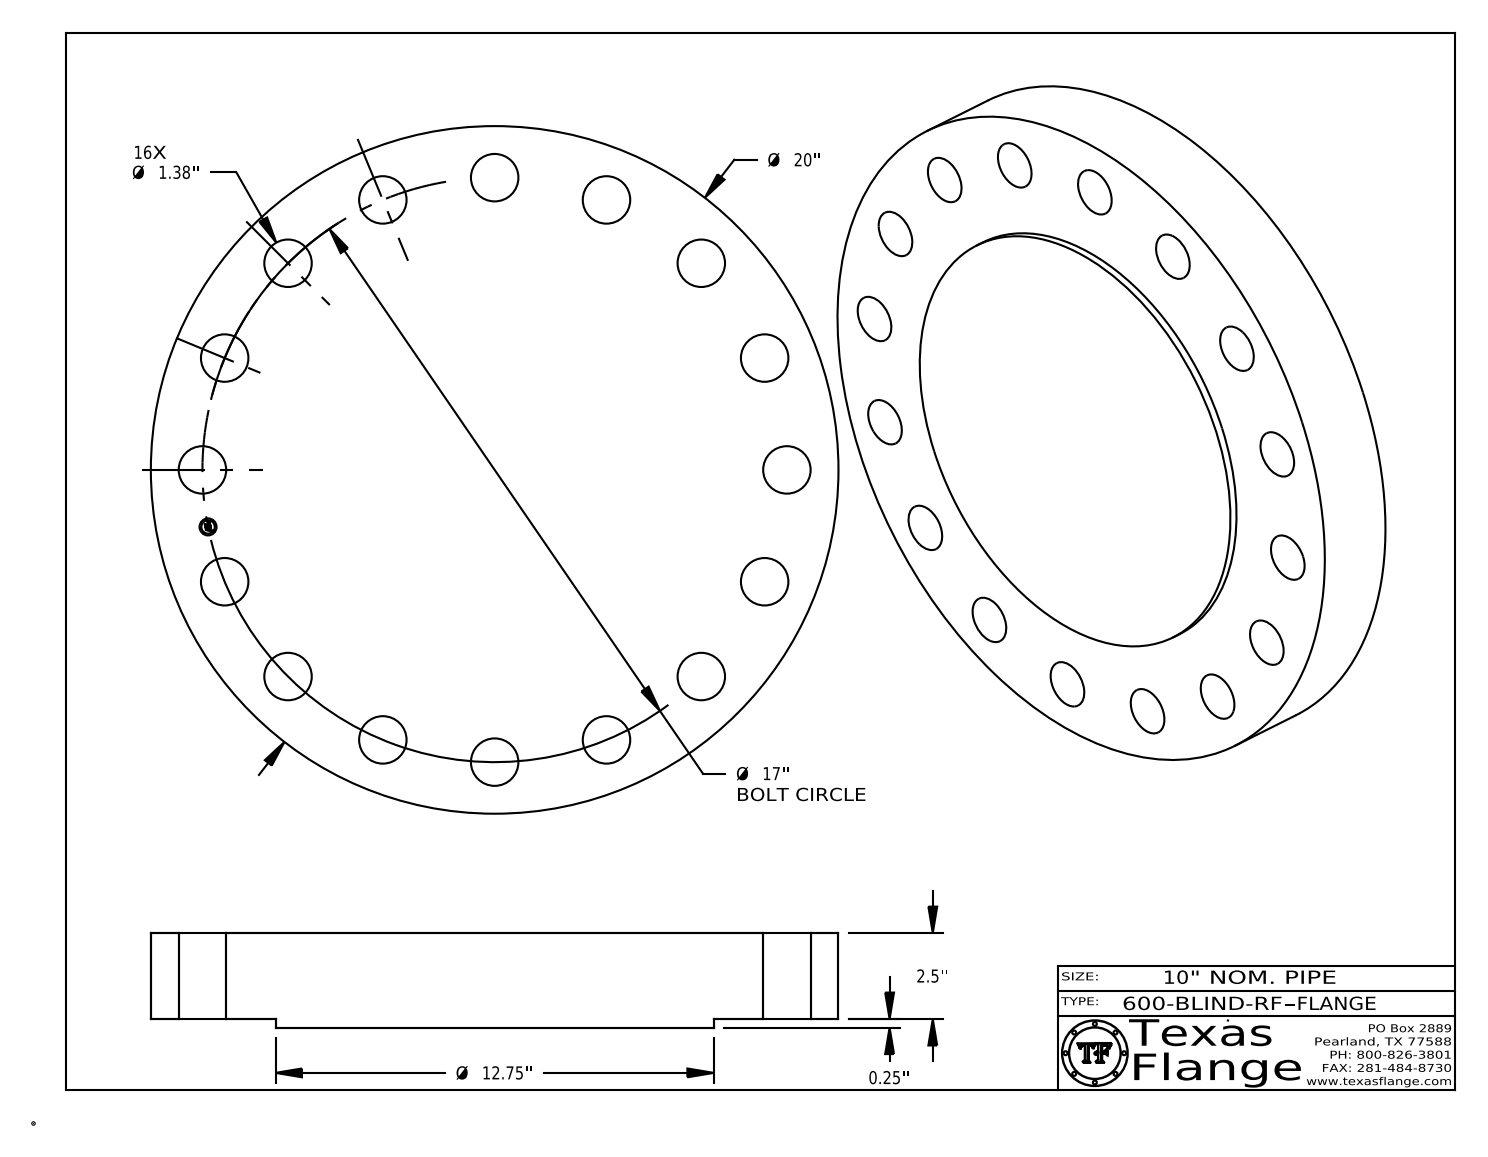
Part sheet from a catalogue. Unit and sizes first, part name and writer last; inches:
Units: inches
Overall size (bounding box): 20 × 20 × 2.75
Round holes (diameter × count): ⌀1.38 ×16, ⌀0.495 ×1
Round bosses / shafts (diameter × count): ⌀0.03 ×8, ⌀20 ×1, ⌀12.75 ×1, ⌀0.39 ×1
Main face-to-face distances: 2.5, 0.25, 2.75, 2.735, 2.485, 0.015, 0.148, 0.145, 0.027, 0.096
Hole centre spacings: 3.317, 14.135, 6.506, 12.021, 9.444, 9.445, 15.706, 15.706
Volume: 757.5 in³ · Surface area: 921.1 in²
Bodies: 1 solid, 424 faces (368 planar, 56 cylindrical, 0 other)
Part name (STEP PRODUCT): 600-BLIND-RF
STEP written by: CATIA V5 STEP AP214 (AUTOMOTIVE_DESIGN)
